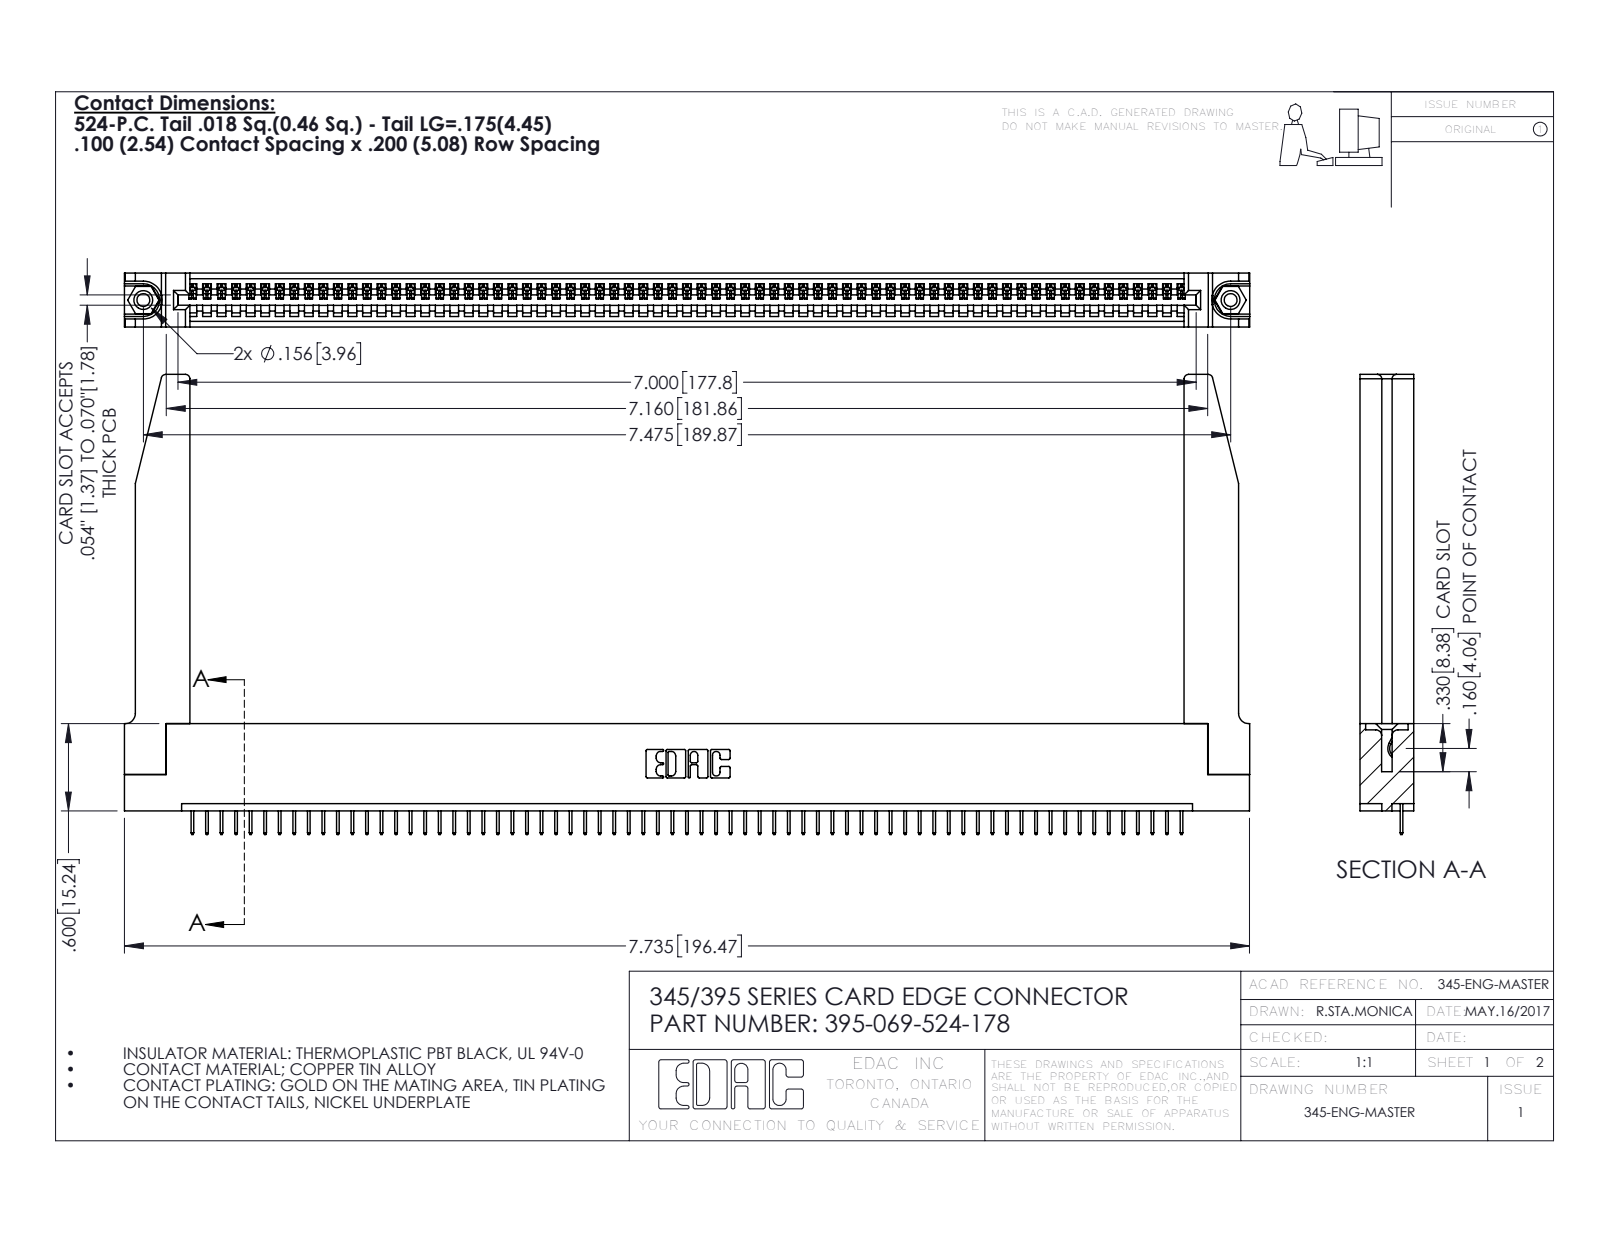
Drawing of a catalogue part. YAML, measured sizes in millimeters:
part_name: "345 Part_Flush Mounting Lugs - 0.156 Dia-TH; 345-292-001_345-293-124; 345-250-001_345-250-001-102; 395-069-524-178 (+1 more)"
step_written_by: "SolidWorks 2016 (CONFIG_CONTROL_DESIGN)"
units: millimeters
bodies: {solids: 74, faces: 4638, planar: 3396, cylindrical: 1190, other: 52}
overall_size: [196.5, 80.3, 9.4]
volume: 26380
surface_area: 31080
round_holes:
  - {diameter: 2.3, count: 2}
  - {diameter: 3.2, count: 2}
  - {diameter: 4, count: 2}
  - {diameter: 1.6, count: 1}
round_bosses_or_shafts:
  - {diameter: 3.9, count: 2}
partial_cylinders:
  - {radius: 0.2, count: 138}
  - {radius: 0.3, count: 22}
  - {radius: 0.8, count: 8}
  - {radius: 0.2, count: 6}
  - {radius: 0.8, count: 6}
  - {radius: 0.7, count: 3}
  - {radius: 0.8, count: 2}
  - {radius: 1, count: 2}
face_to_face_distances: [9.4, 1.8, 7.6, 5.1, 2.5, 6.9, 0.6, 5.7, 1.8, 3.8]
hole_center_spacings: [6.9, 183.9, 189.9]
